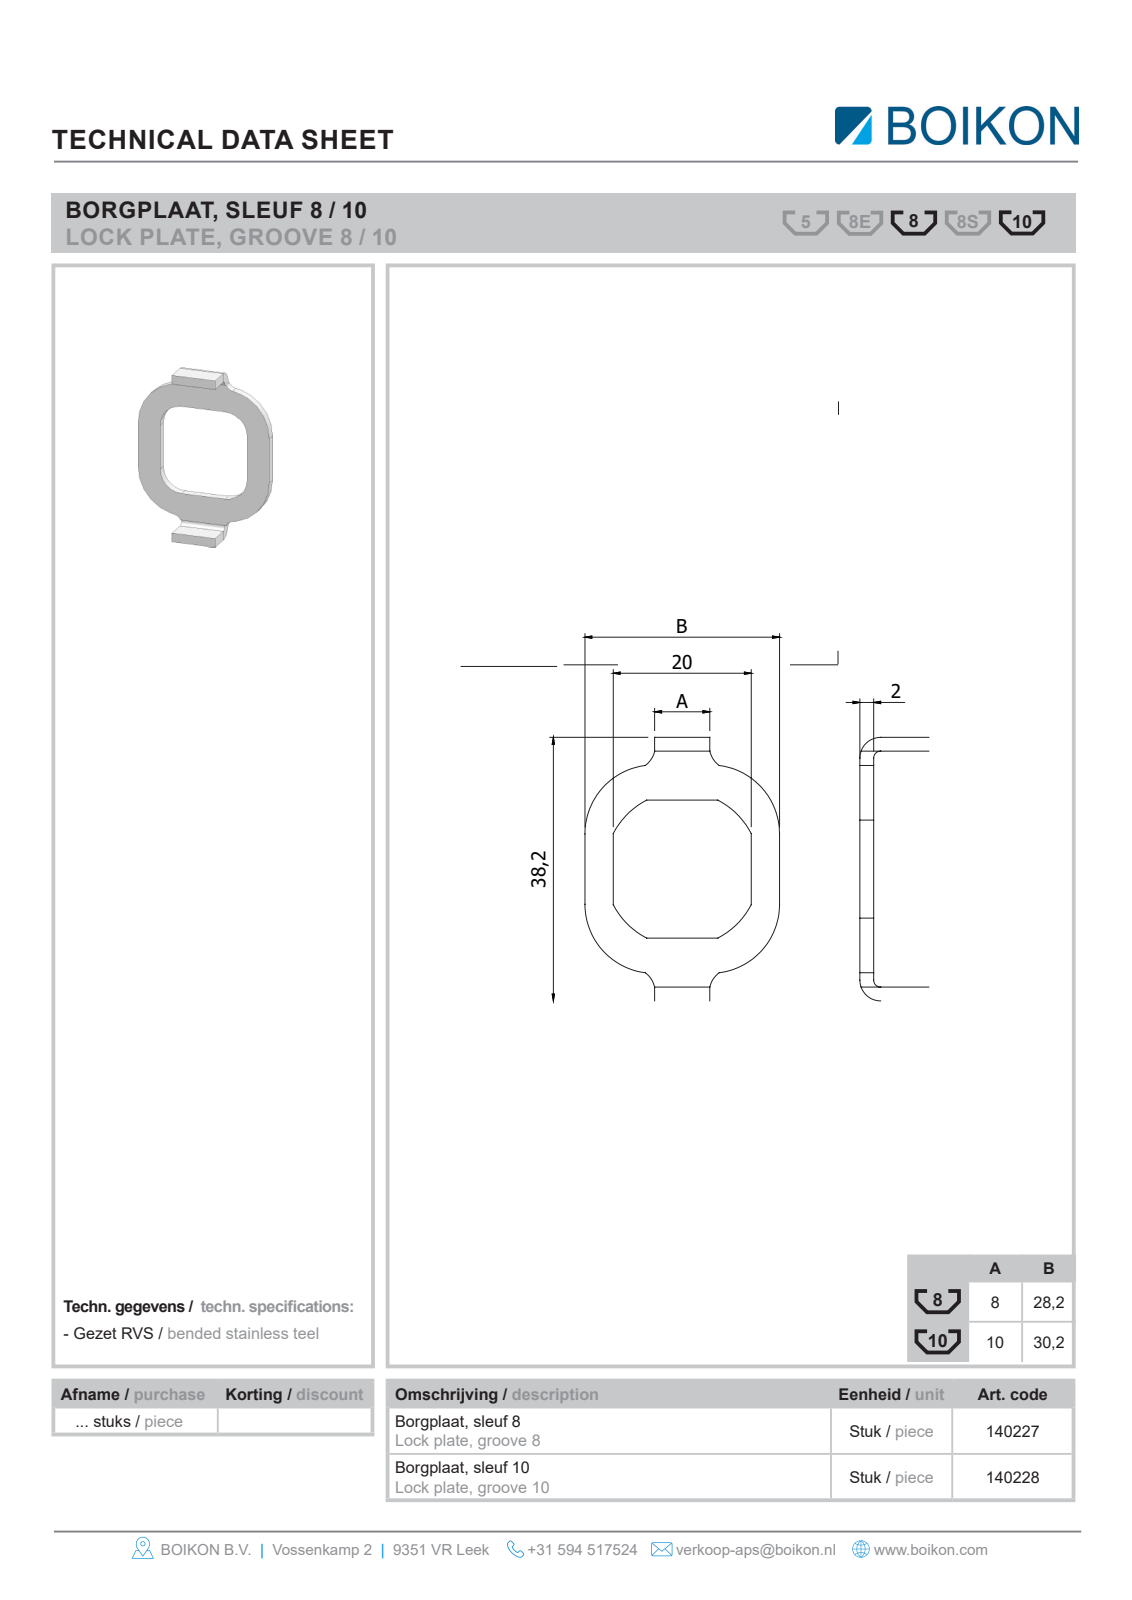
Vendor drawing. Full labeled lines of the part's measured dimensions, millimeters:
Part name (STEP PRODUCT): Root; 140228Borgplaat, sleuf 10BOIKON; Bend zone; Sheet flange
STEP written by: HiCAD 2013 1802.4 Build 509 (AUTOMOTIVE_DESIGN)
Units: millimetres
Bodies: 5 solids, 47 faces (31 planar, 16 cylindrical, 0 other)
Overall size (bounding box): 38.2 × 30.2 × 8
Volume: 1 267 mm³ · Surface area: 1 845 mm²
Partial cylindrical surfaces — rounded edges, fillets, slot ends (radius × count): R2 ×4, R5 ×4, R10 ×4, R1 ×2, R3 ×2
Main face-to-face distances: 2, 3, 1, 36.2, 35.2, 33.2, 5, 38.2, 34.2, 32.2
